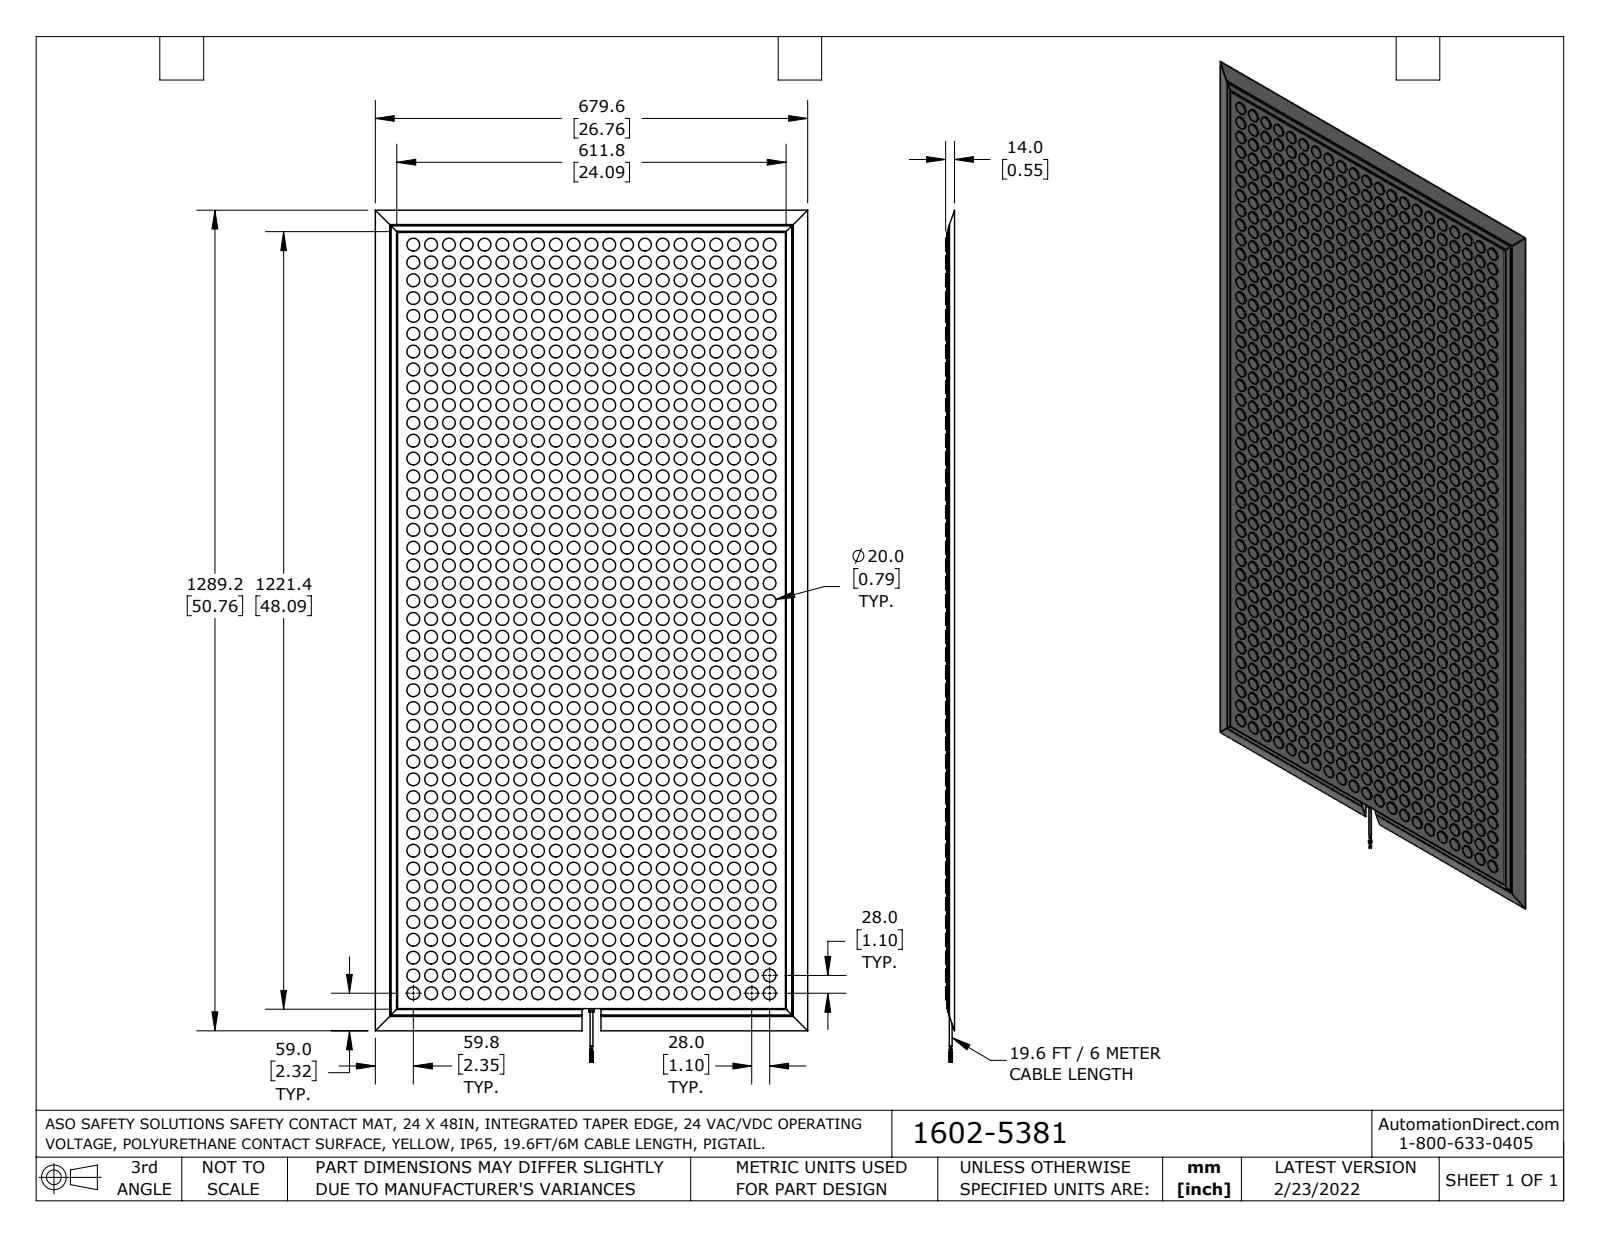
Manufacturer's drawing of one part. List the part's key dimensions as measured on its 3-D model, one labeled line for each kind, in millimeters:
Part name (STEP PRODUCT): 1602-5381_Default
STEP written by: SolidWorks 2021 (CONFIG_CONTROL_DESIGN)
Units: millimetres
Bodies: 3 solids, 2882 faces (961 planar, 1889 cylindrical, 32 other)
Overall size (bounding box): 1338.2 × 679.6 × 14
Volume: 10 240 000 mm³ · Surface area: 1 916 000 mm²
Round holes (diameter × count): ⌀4.4 ×1
Round bosses / shafts (diameter × count): ⌀20 ×903, ⌀1.2 ×20, ⌀0.8 ×8, ⌀8 ×1, ⌀7 ×1
Partial cylindrical surfaces — rounded edges, fillets, slot ends (radius × count): R0.2 ×4
Main face-to-face distances: 12, 14, 2, 6, 609.6, 8, 1219.2, 289.8, 319.8, 30
